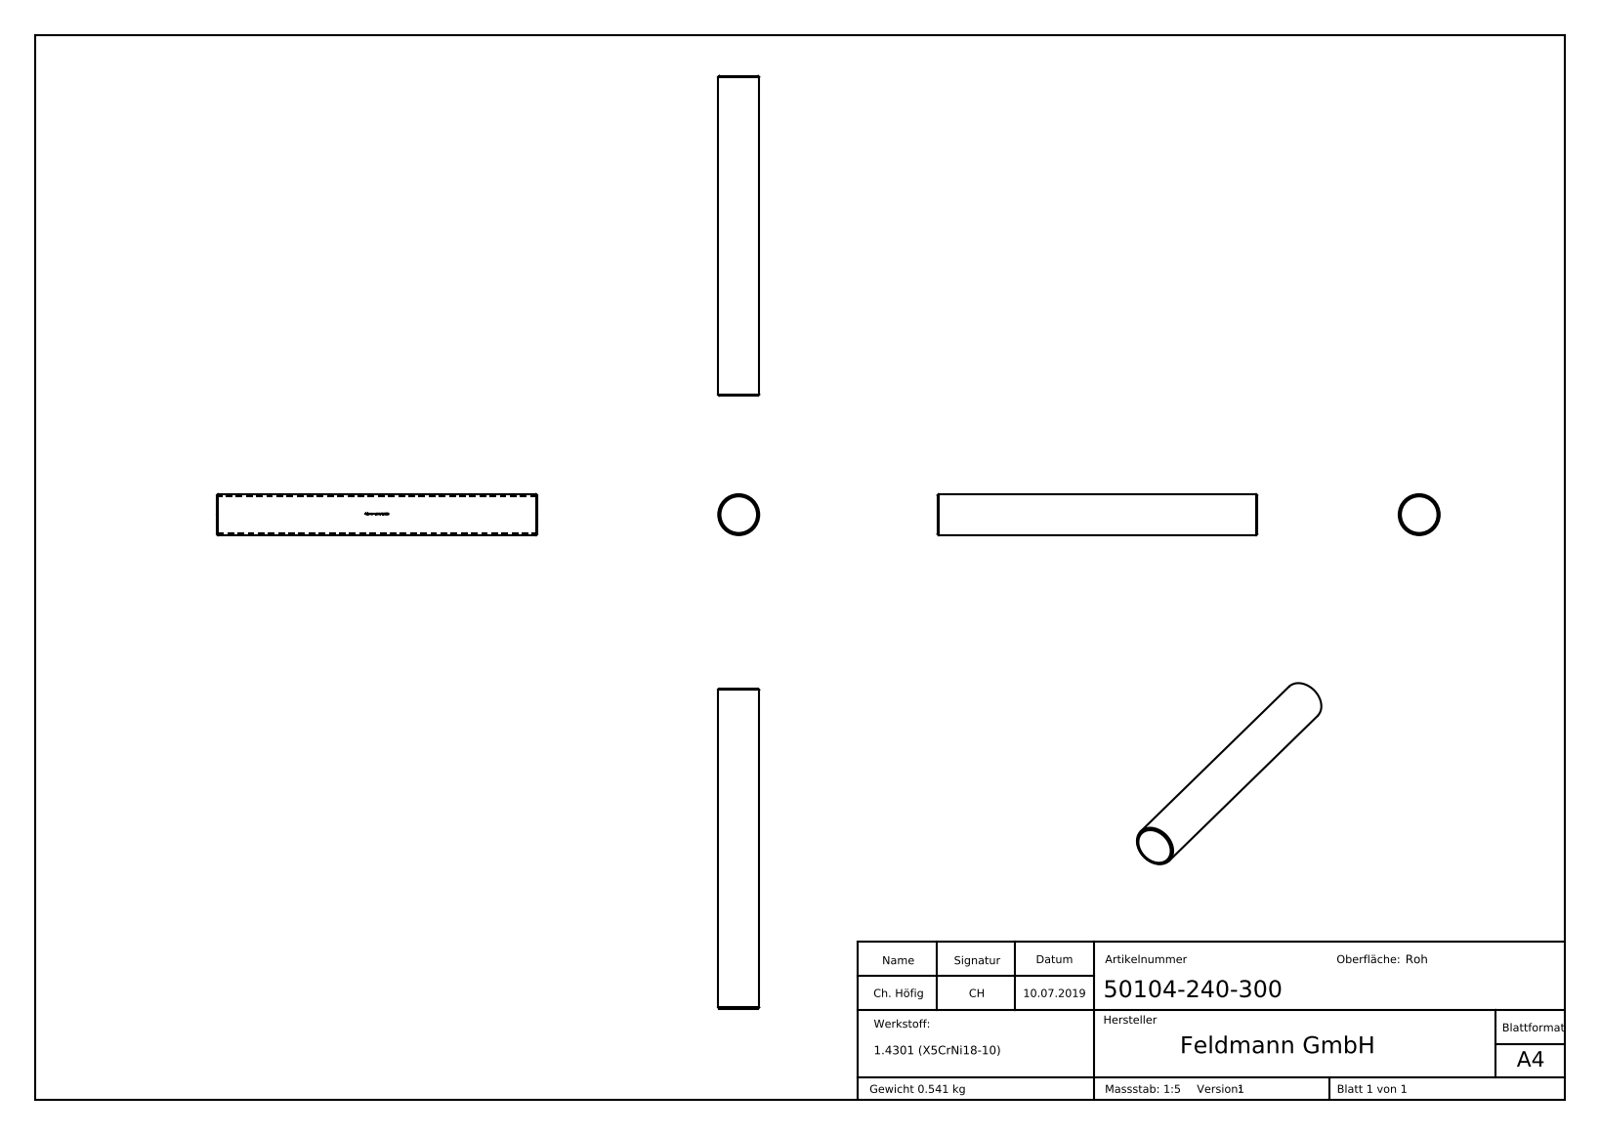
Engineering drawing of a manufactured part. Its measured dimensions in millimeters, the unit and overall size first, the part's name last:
Units: millimetres
Overall size (bounding box): 300 × 38.4 × 38.4
Round holes (diameter × count): ⌀34.4 ×1
Round bosses / shafts (diameter × count): ⌀38.4 ×1
Partial cylindrical surfaces — rounded edges, fillets, slot ends (radius × count): R17.3 ×1
Main face-to-face distances: 300, 0.44, 0.88, 9.72, 2.97, 0.58, 1.26, 4.9, 14.62, 2.64
Volume: 68 493 mm³ · Surface area: 68 937 mm²
Bodies: 1 solid, 287 faces (111 planar, 51 cylindrical, 125 other)
Part name (STEP PRODUCT): 50104-240-300
STEP written by: SolidWorks 2015 (CONFIG_CONTROL_DESIGN)
